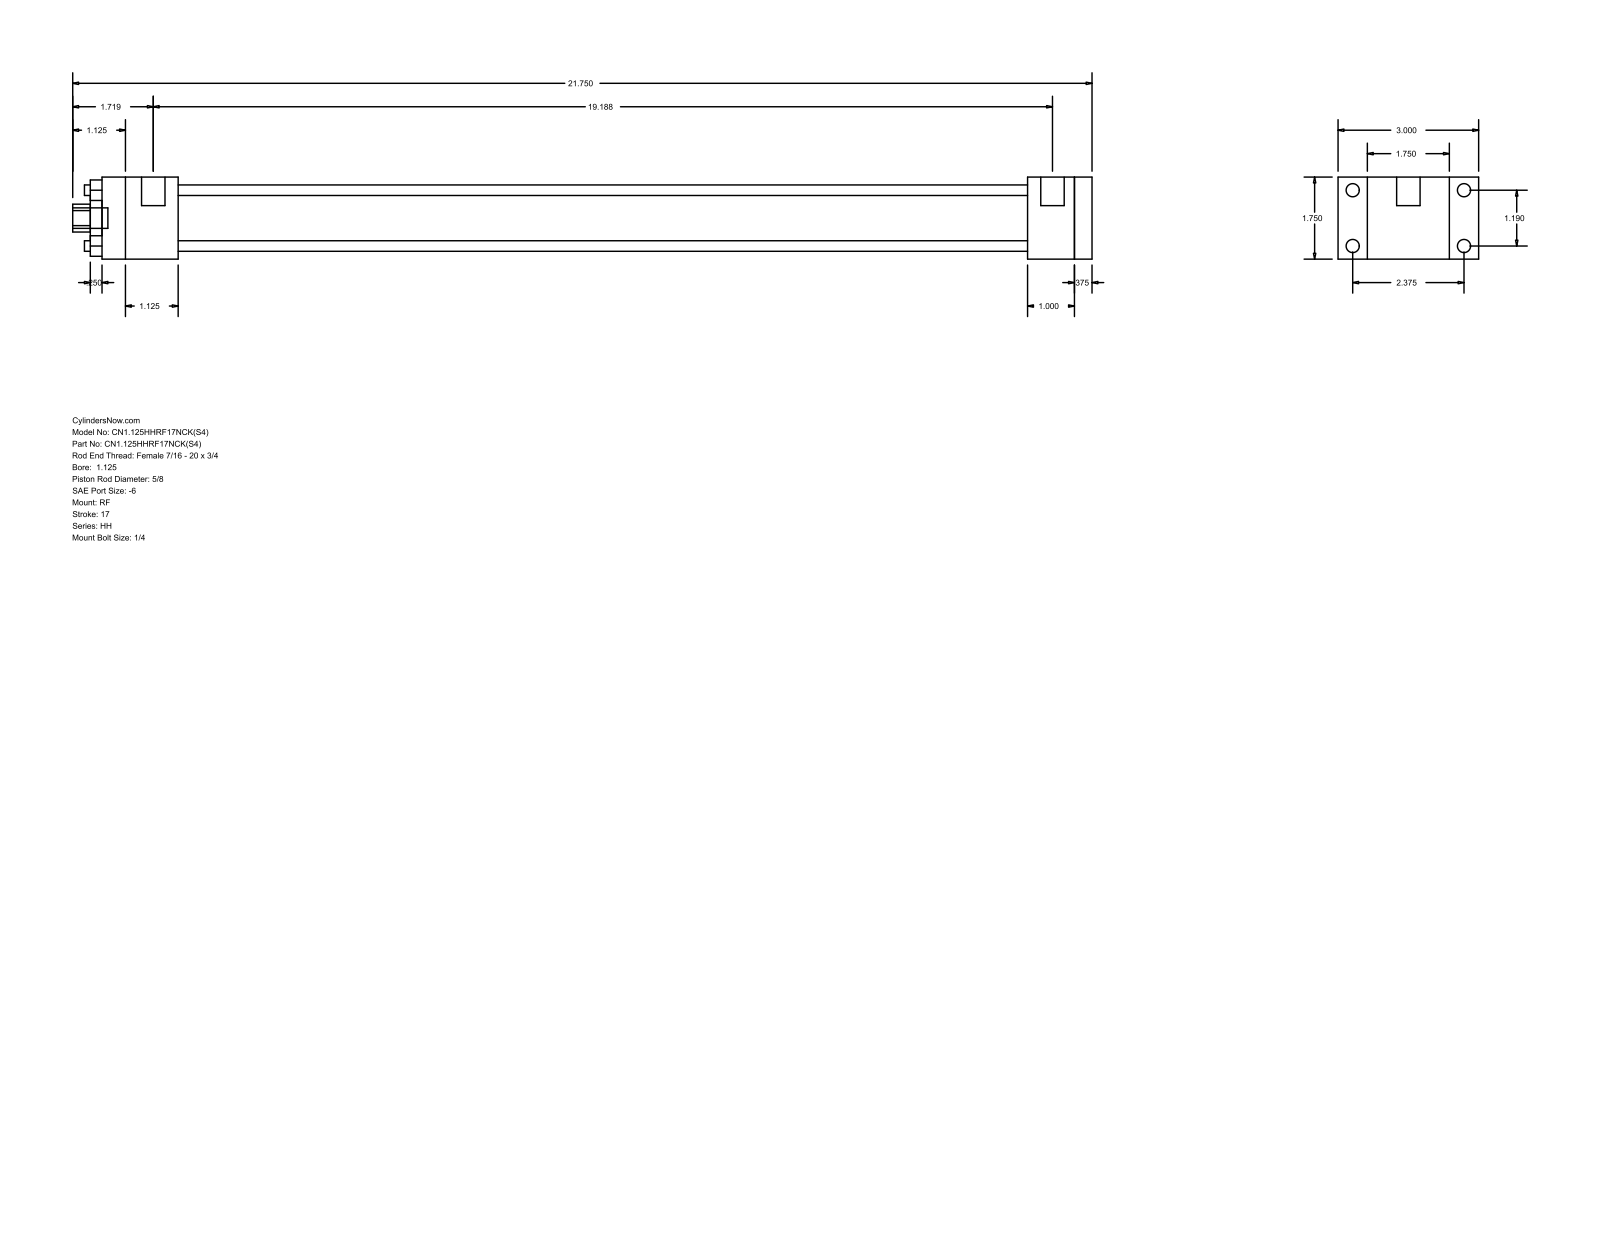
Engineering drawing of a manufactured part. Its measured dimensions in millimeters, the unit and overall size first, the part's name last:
Units: millimetres
Overall size (bounding box): 552.45 × 76.2 × 44.45
Round holes (diameter × count): ⌀5.71 ×4, ⌀15.88 ×1, ⌀28.57 ×1, ⌀34.92 ×1
Round bosses / shafts (diameter × count): ⌀7.14 ×4, ⌀5.56 ×4, ⌀12.7 ×2, ⌀11.11 ×1
Partial cylindrical surfaces — rounded edges, fillets, slot ends (radius × count): R7.54 ×1
Main face-to-face distances: 44.46, 9.53, 536.57, 15.87, 485.77, 495.3, 460.37, 25.4, 34.93, 41.27
Hole centre spacings: 21.37, 30.22, 42.74
Bodies: 0 solids, 92 faces (64 planar, 28 cylindrical, 0 other)
Part name (STEP PRODUCT): HH_RF__0112_0.625
STEP written by: GSSL Pune (CONFIG_CONTROL_DESIGN)
